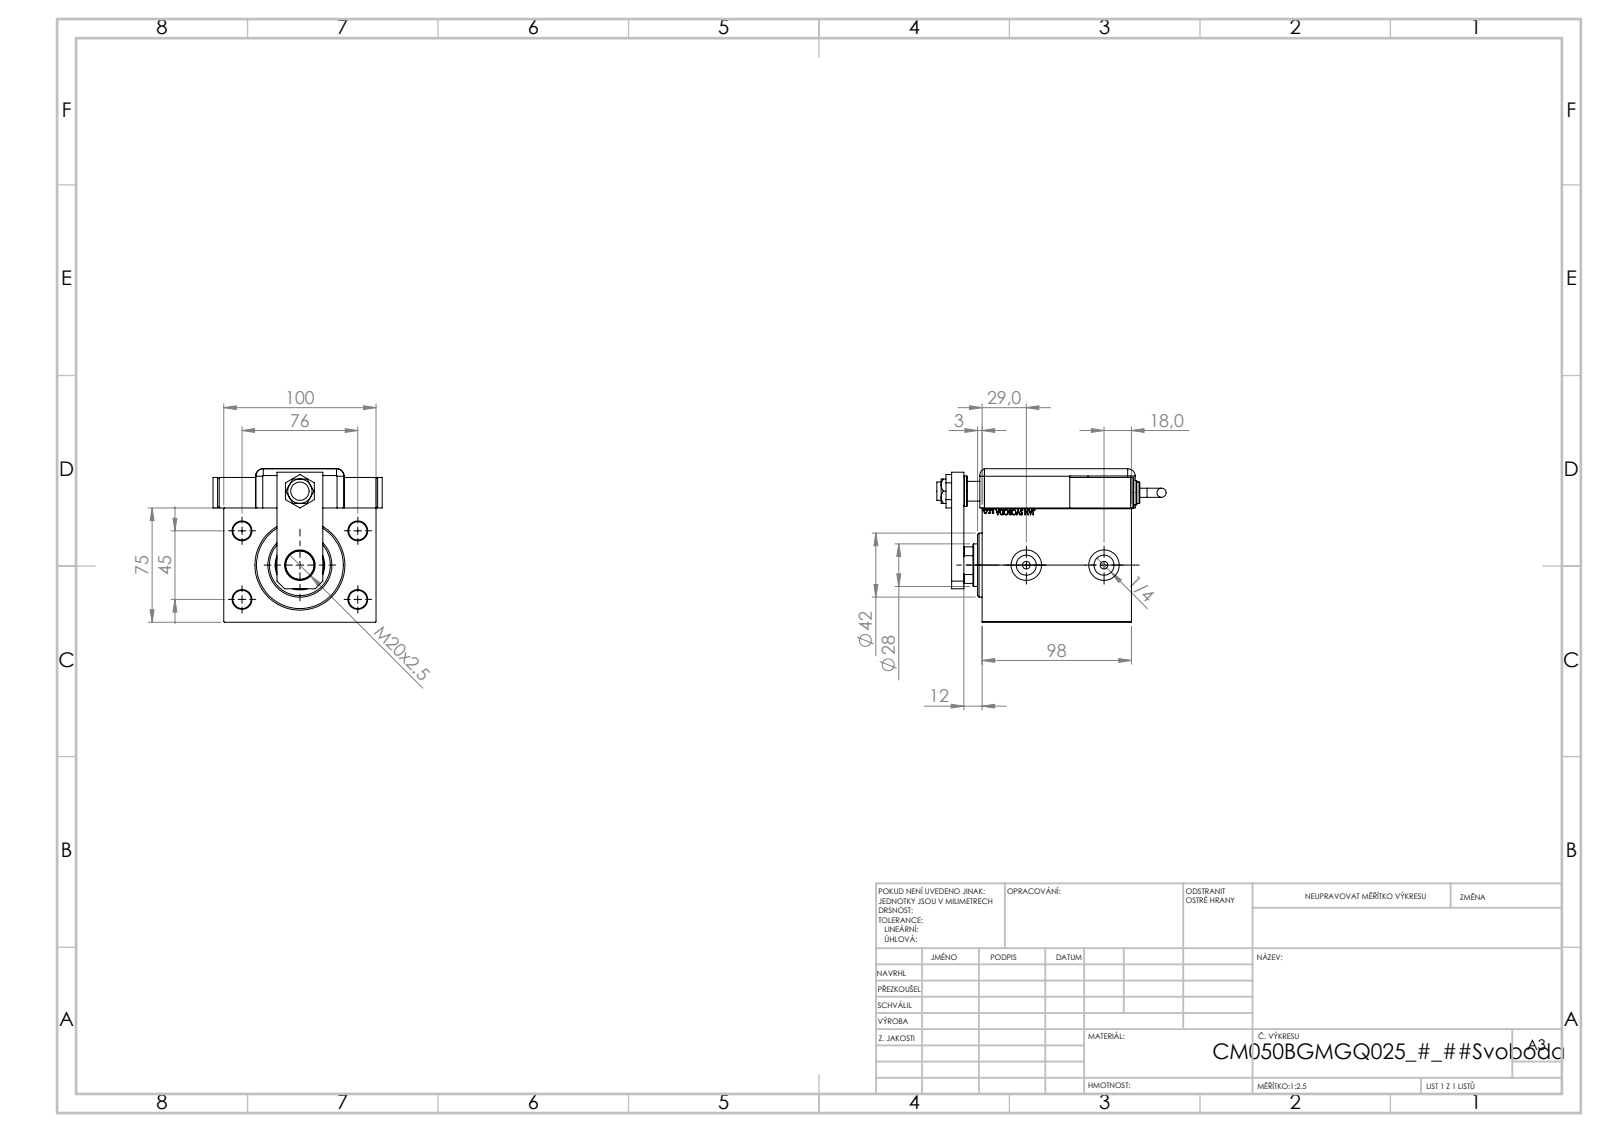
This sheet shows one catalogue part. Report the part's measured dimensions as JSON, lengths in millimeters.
{"part_name": "NUT_D19; V450CM_B_VCP; SWITCH Q; MAGNETIC SWITCH Q (+7 more)", "step_written_by": "SolidWorks 2019 (CONFIG_CONTROL_DESIGN)", "units": "millimeters", "bodies": {"solids": 13, "faces": 1268, "planar": 608, "cylindrical": 111, "other": 549}, "overall_size": [150.46, 111, 100.8], "volume_mm3": 821004, "surface_area_mm2": 148927, "round_holes": [[12, 5], [20, 3], [4, 2], [5, 2], [8, 2], [13.16, 2], [13, 1], [14, 1], [18.5, 1], [28, 1], [31.5, 1], [32.5, 1]], "round_bosses_or_shafts": [[20, 3], [16, 2], [14, 2], [6, 2], [42, 1]], "partial_cylinders_radius": [[5, 9], [10, 1], [13.5, 1]], "face_to_face_distances": [75, 3, 98, 100, 14, 20, 84, 25.8, 100.8, 13.5], "hole_center_spacings": [44.16, 45, 46.04, 76, 80.53, 88.32, 20, 48.5]}
